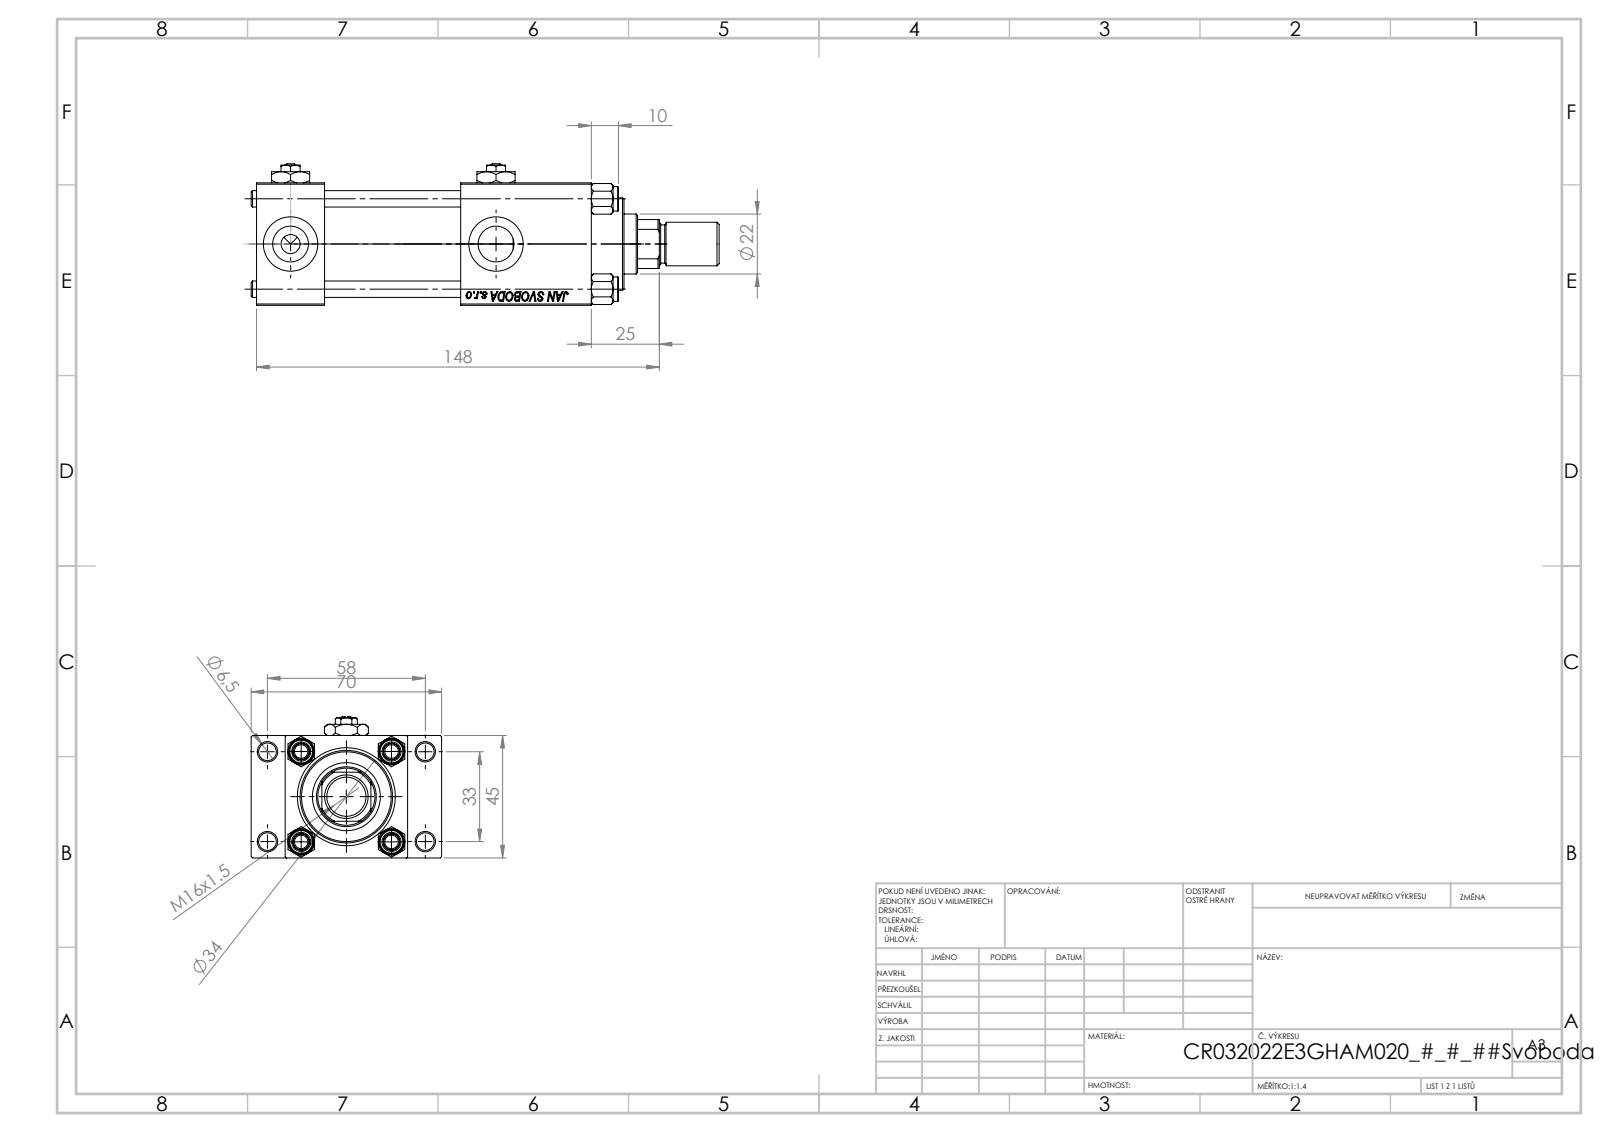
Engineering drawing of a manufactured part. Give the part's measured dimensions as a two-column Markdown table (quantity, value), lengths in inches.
| quantity | value |
| --- | --- |
| part name | V215CR_VCP_E; V215_VC_A; NUT_M5_E; V215CR_E_Body (+3 more) |
| STEP written by | SolidWorks 2019 (CONFIG_CONTROL_DESIGN) |
| units | inches |
| bodies | 14 solids, 1249 faces (548 planar, 101 cylindrical, 600 other) |
| overall size | 6.772 × 2.756 × 2.047 |
| volume | 14.56 in³ |
| surface area | 130.7 in² |
| round holes (diameter × count) | 0.236 × 4, 0.256 × 4, 0.518 × 4, 0.787 × 4, 0.276 × 3, 0.413 × 1, 0.866 × 1, 0.945 × 1, 0.984 × 1, 1.26 × 1, 1.299 × 1 |
| round bosses / shafts (diameter × count) | 0.354 × 4, 1.496 × 1, 1.339 × 1, 0.63 × 1, 0.551 × 1 |
| partial cylindrical surfaces (radius × count) | 0.413 × 1 |
| main face-to-face distances | 1.772, 0.984, 0.492, 2.264, 4.843, 1.969, 2.953, 3.858, 1.89, 2.756 |
| hole center spacings | 0.488, 0.924, 1.307, 1.314, 1.392, 1.795, 2.219, 1.299 |
